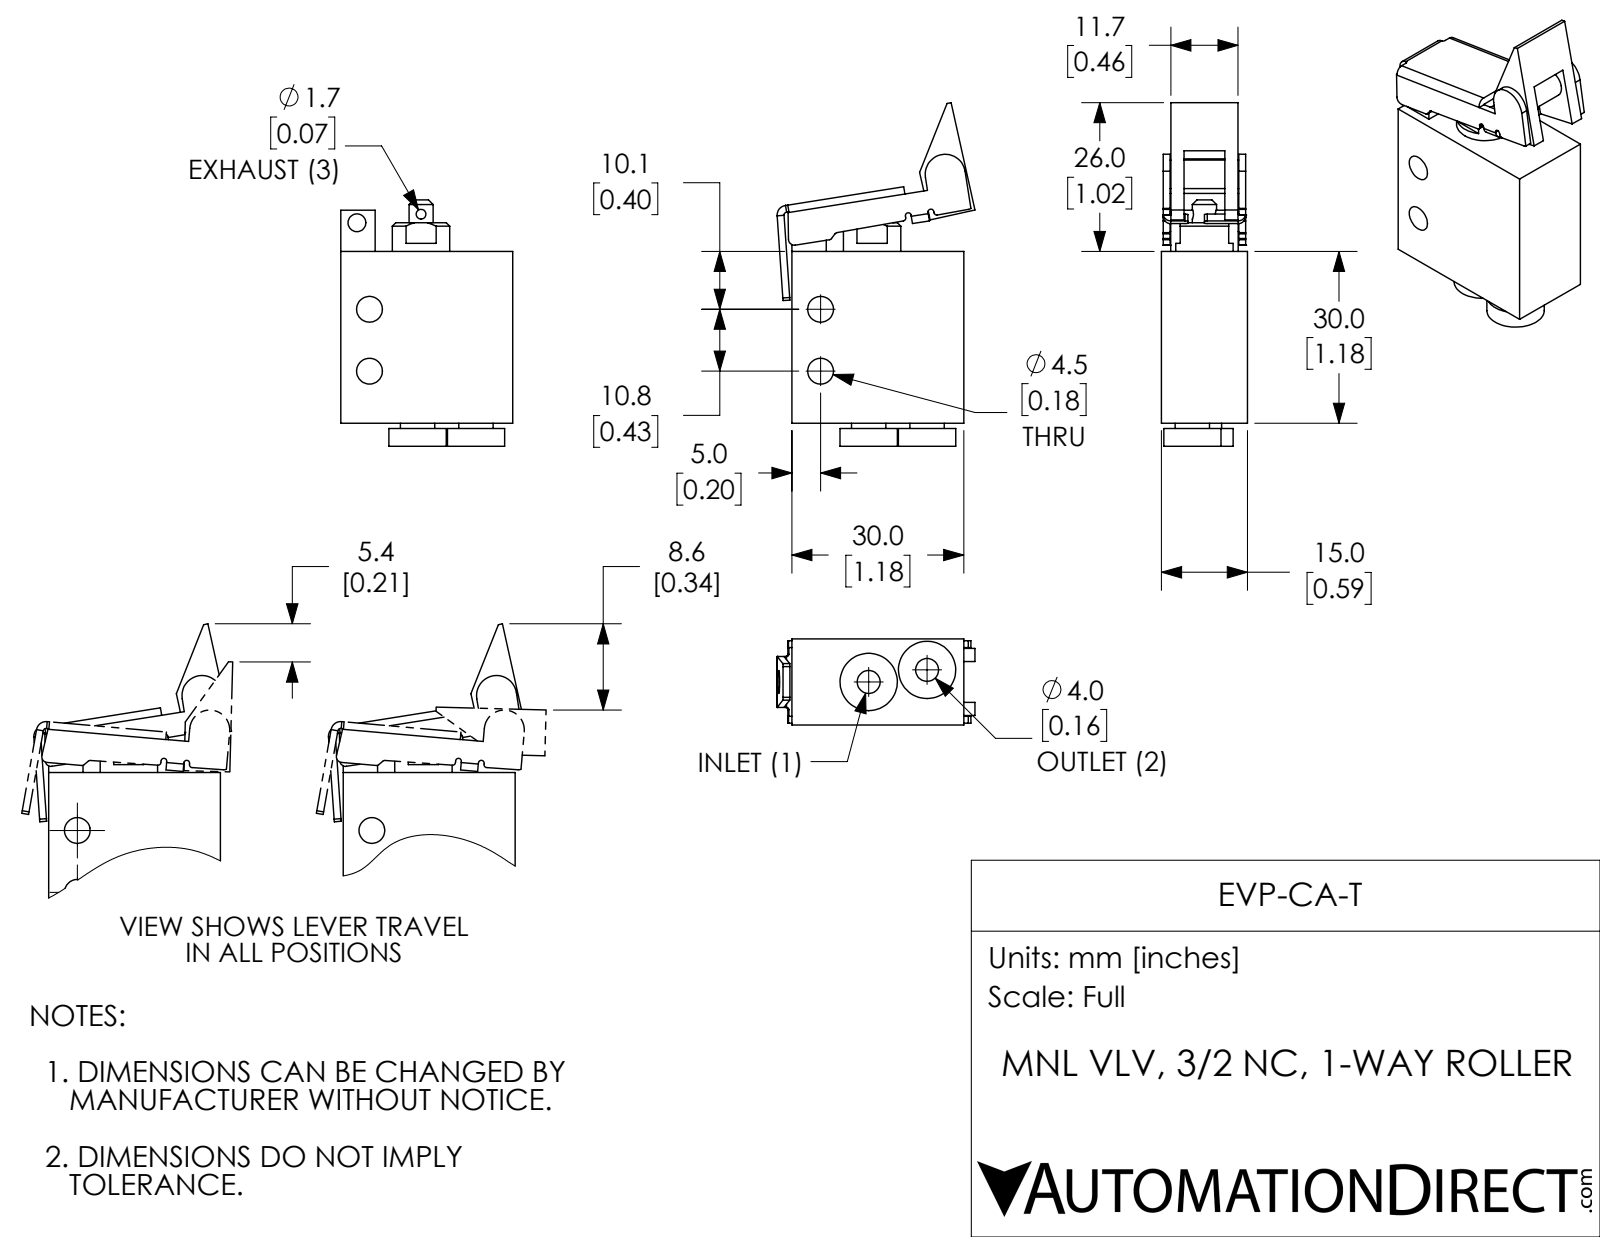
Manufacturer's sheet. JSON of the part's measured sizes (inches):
{"part_name": "EVP-CA-T", "step_written_by": "SolidWorks 2017 (AUTOMOTIVE_DESIGN)", "units": "inches", "bodies": {"solids": 3, "faces": 154, "planar": 82, "cylindrical": 68, "other": 4}, "overall_size": [2.361, 1.36, 0.591], "volume_in3": 0.992, "surface_area_in2": 12.41, "round_holes": [[0.157, 3], [0.177, 2], [0.067, 1], [0.122, 1], [0.197, 1]], "round_bosses_or_shafts": [[0.394, 3], [0.236, 2], [0.165, 1]], "partial_cylinders_radius": [[0.02, 13], [0.051, 4], [0.004, 2], [0.016, 2], [0.039, 2], [0.067, 1], [0.138, 1]], "face_to_face_distances": [0.591, 1.181, 0.579, 0.047, 0.048, 0.059, 0.531, 0.52, 0.065, 0.053], "hole_center_spacings": [0.41, 0.425, 0.445, 0.572, 0.601, 0.743, 1.001, 1.023]}
